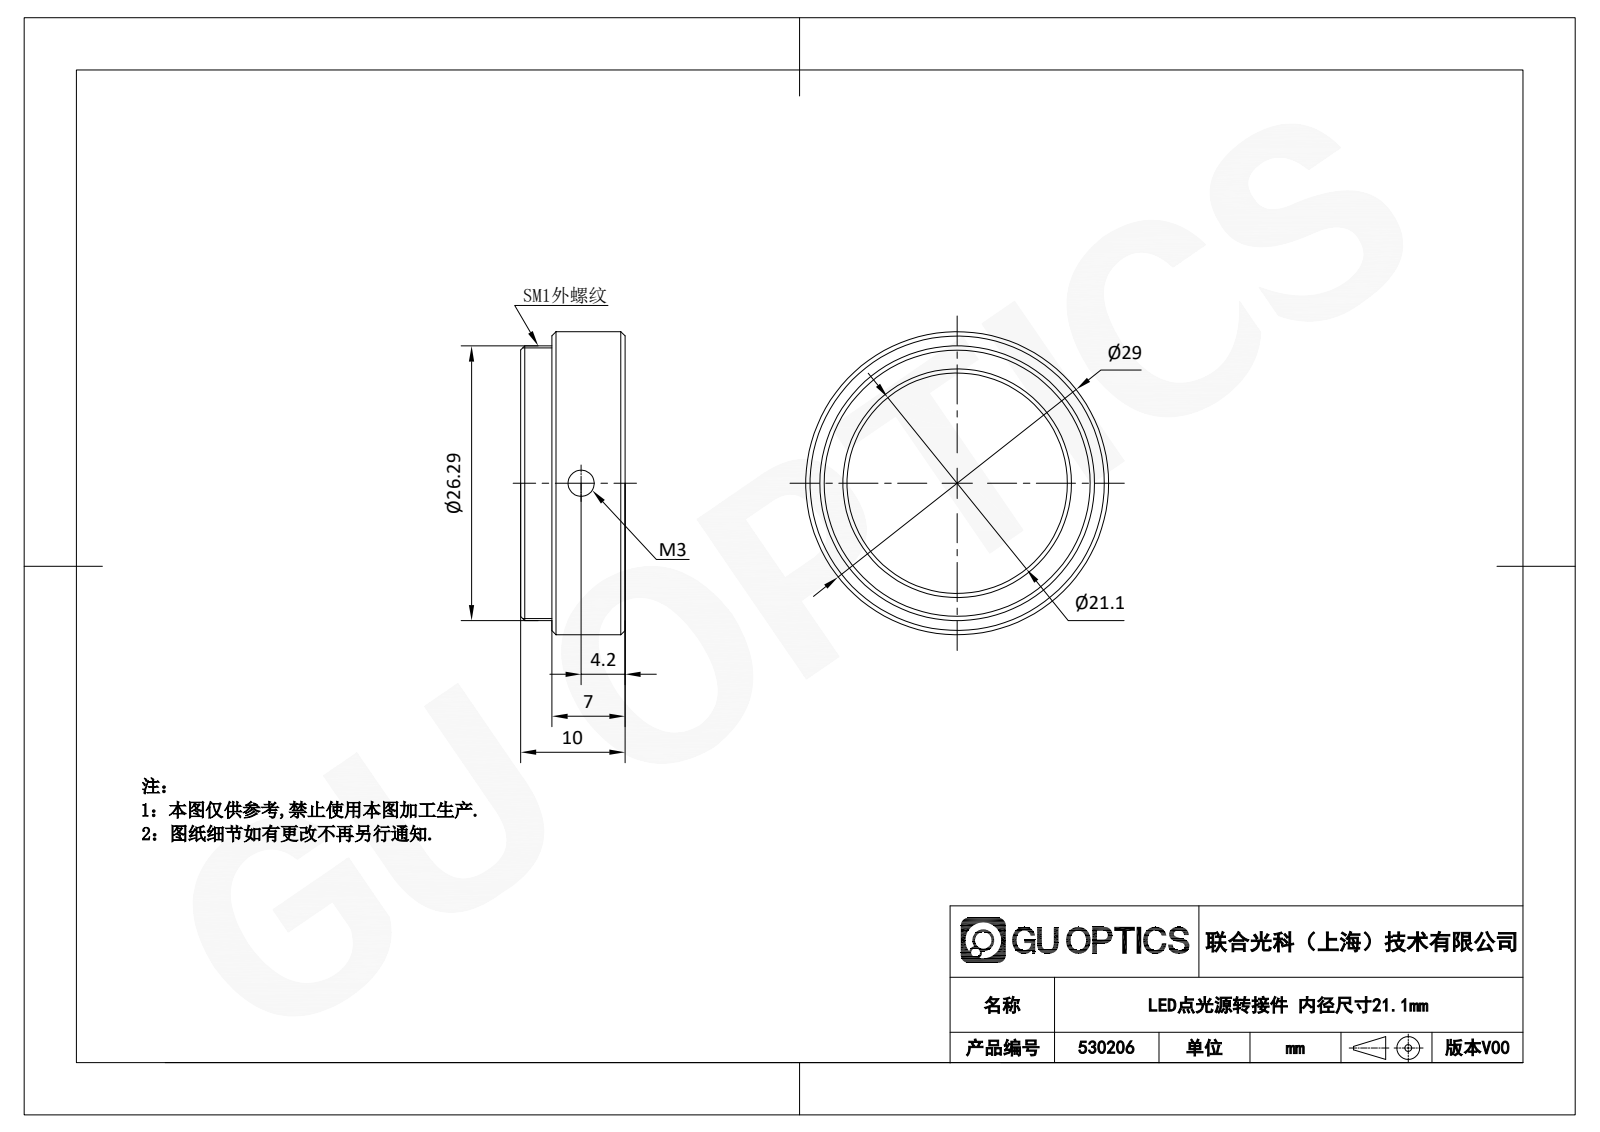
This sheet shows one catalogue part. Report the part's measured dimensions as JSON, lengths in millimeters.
{"part_name": "530206", "step_written_by": "SolidWorks 2020 (CONFIG_CONTROL_DESIGN)", "units": "millimeters", "bodies": {"solids": 1, "faces": 12, "planar": 3, "cylindrical": 4, "other": 5}, "overall_size": [29, 29, 10], "volume_mm3": 2704, "surface_area_mm2": 2098, "round_holes": [[2.5, 1], [21.1, 1]], "round_bosses_or_shafts": [[29, 1], [26.29, 1]], "face_to_face_distances": [10, 3, 7]}
